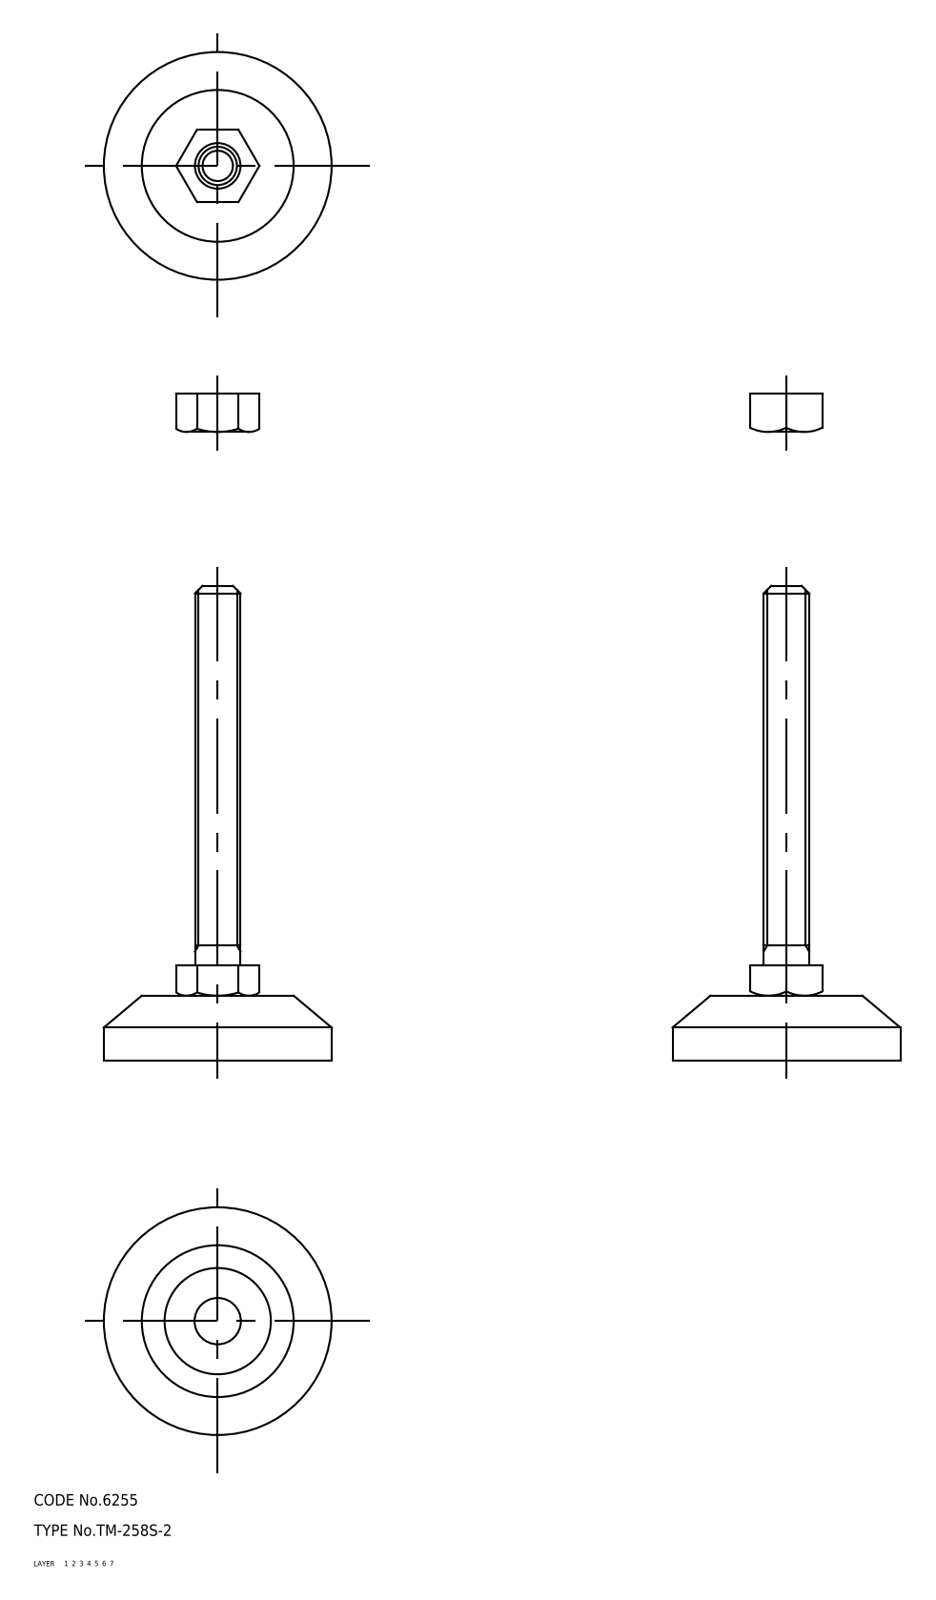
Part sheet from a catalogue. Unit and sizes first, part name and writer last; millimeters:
Units: millimetres
Overall size (bounding box): 125 × 60 × 60
Volume: 47 478 mm³ · Surface area: 15 571 mm²
Bodies: 3 solids, 75 faces (0 planar, 0 cylindrical, 75 other)
Part name (STEP PRODUCT): 67112545; 67112558; 67112571
STEP written by: CADfix (AUTOMOTIVE_DESIGN)
